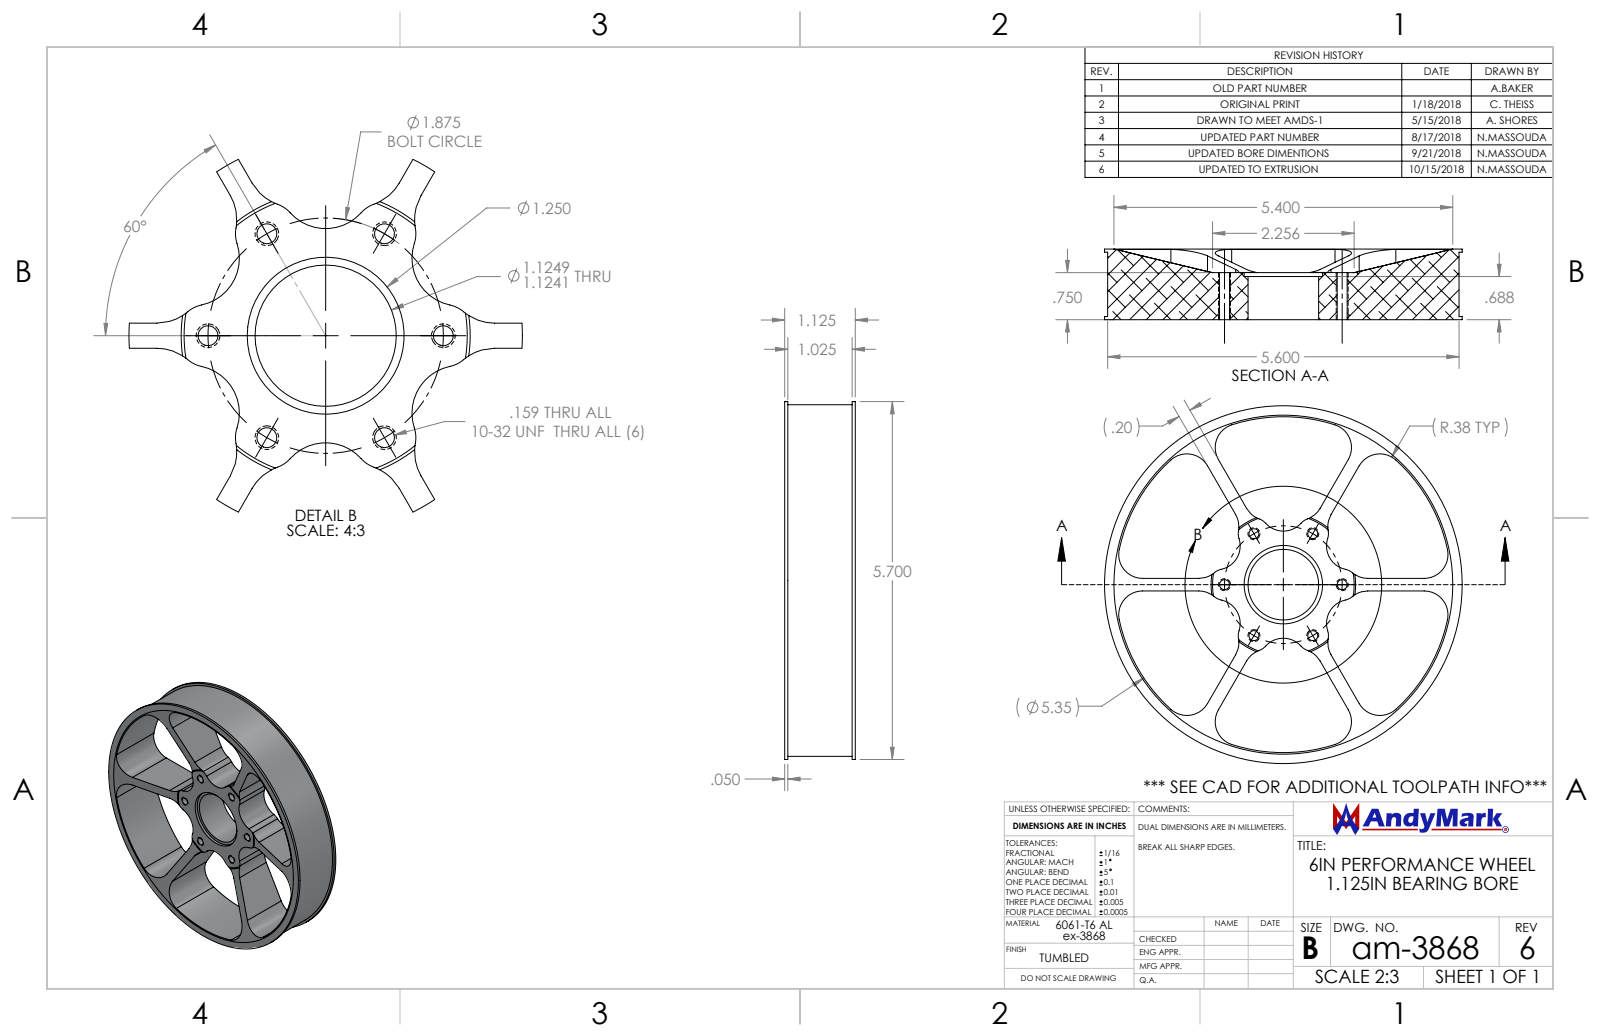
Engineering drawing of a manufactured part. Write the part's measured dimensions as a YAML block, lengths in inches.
part_name: "am-3868 6in Performance Wheel Bearing Bore"
step_written_by: "SolidWorks 2018 (CONFIG_CONTROL_DESIGN)"
units: inches
bodies: {solids: 1, faces: 107, planar: 18, cylindrical: 80, other: 9}
overall_size: [5.7, 5.7, 1.125]
volume: 6.385
surface_area: 77.95
round_holes:
  - {diameter: 0.159, count: 6}
  - {diameter: 1.125, count: 1}
  - {diameter: 1.25, count: 1}
round_bosses_or_shafts:
  - {diameter: 5.7, count: 1}
  - {diameter: 5.6, count: 1}
partial_cylinders:
  - {radius: 0.38, count: 30}
  - {radius: 0.25, count: 6}
  - {radius: 2.675, count: 1}
face_to_face_distances: [0.2, 1.125, 0.375, 0.75, 0.05, 1.075, 0.325, 1.025, 0.7, 0.437]
hole_center_spacings: [0.937, 1.624, 1.875, 0.938]
